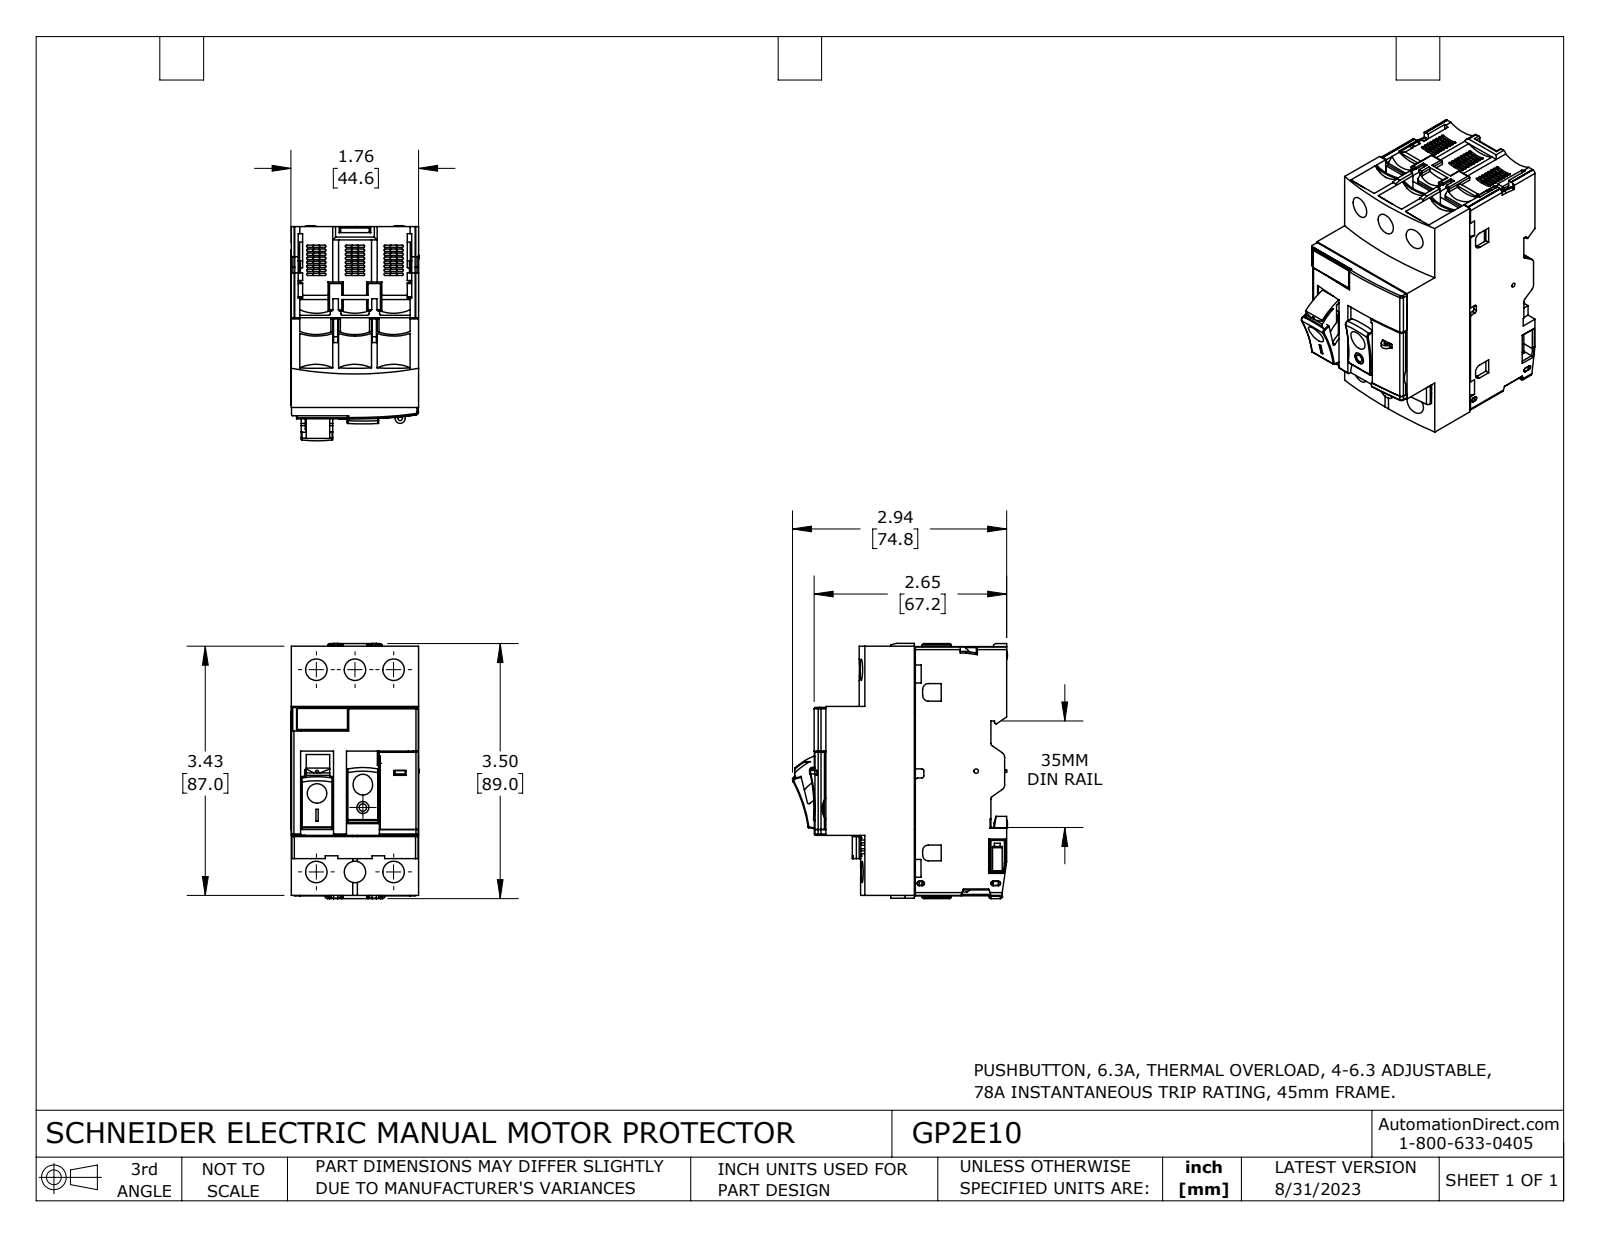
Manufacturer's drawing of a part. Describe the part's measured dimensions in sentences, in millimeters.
The part is named "GP2E10". Its 3-D file was written by "SolidWorks 2021 (CONFIG_CONTROL_DESIGN)". It is 15 solids with 2269 faces: 1521 planar, 657 cylindrical and 91 other. Overall it measures 89.1 by 75.1 by 44.8 millimeters. Its volume is 189 800 cubic millimeters and its surface area 63 830 square millimeters. Round holes: 6 of diameter 7.5, 5 of diameter 5, 2 of diameter 1.5, 1 of diameter 4, 1 of diameter 4.2, 1 of diameter 8, 1 of diameter 8.3, 1 of diameter 8.5, 1 of diameter 8.7. Round bosses or shafts: 2 of diameter 6.2, 2 of diameter 3, 1 of diameter 9.7, 1 of diameter 2.6, 1 of diameter 1.2. Partial cylindrical surfaces (rounded edges, fillets, slot ends): 104 of radius 0.4, 47 of radius 0.5, 16 of radius 1, 12 of radius 0.3, 12 of radius 0.3, 12 of radius 0.8, 8 of radius 1.5, 6 of radius 0.1. The main face-to-face distances are 44.5, 13.5, 2.9, 31.3, 44.6, 1.5, 41.6, 14.8, 26.7, 29.7. The hole center spacings are 13.5, 71.9, 70.6, 8.8, 10.2, 13.9, 17, 18.4.
